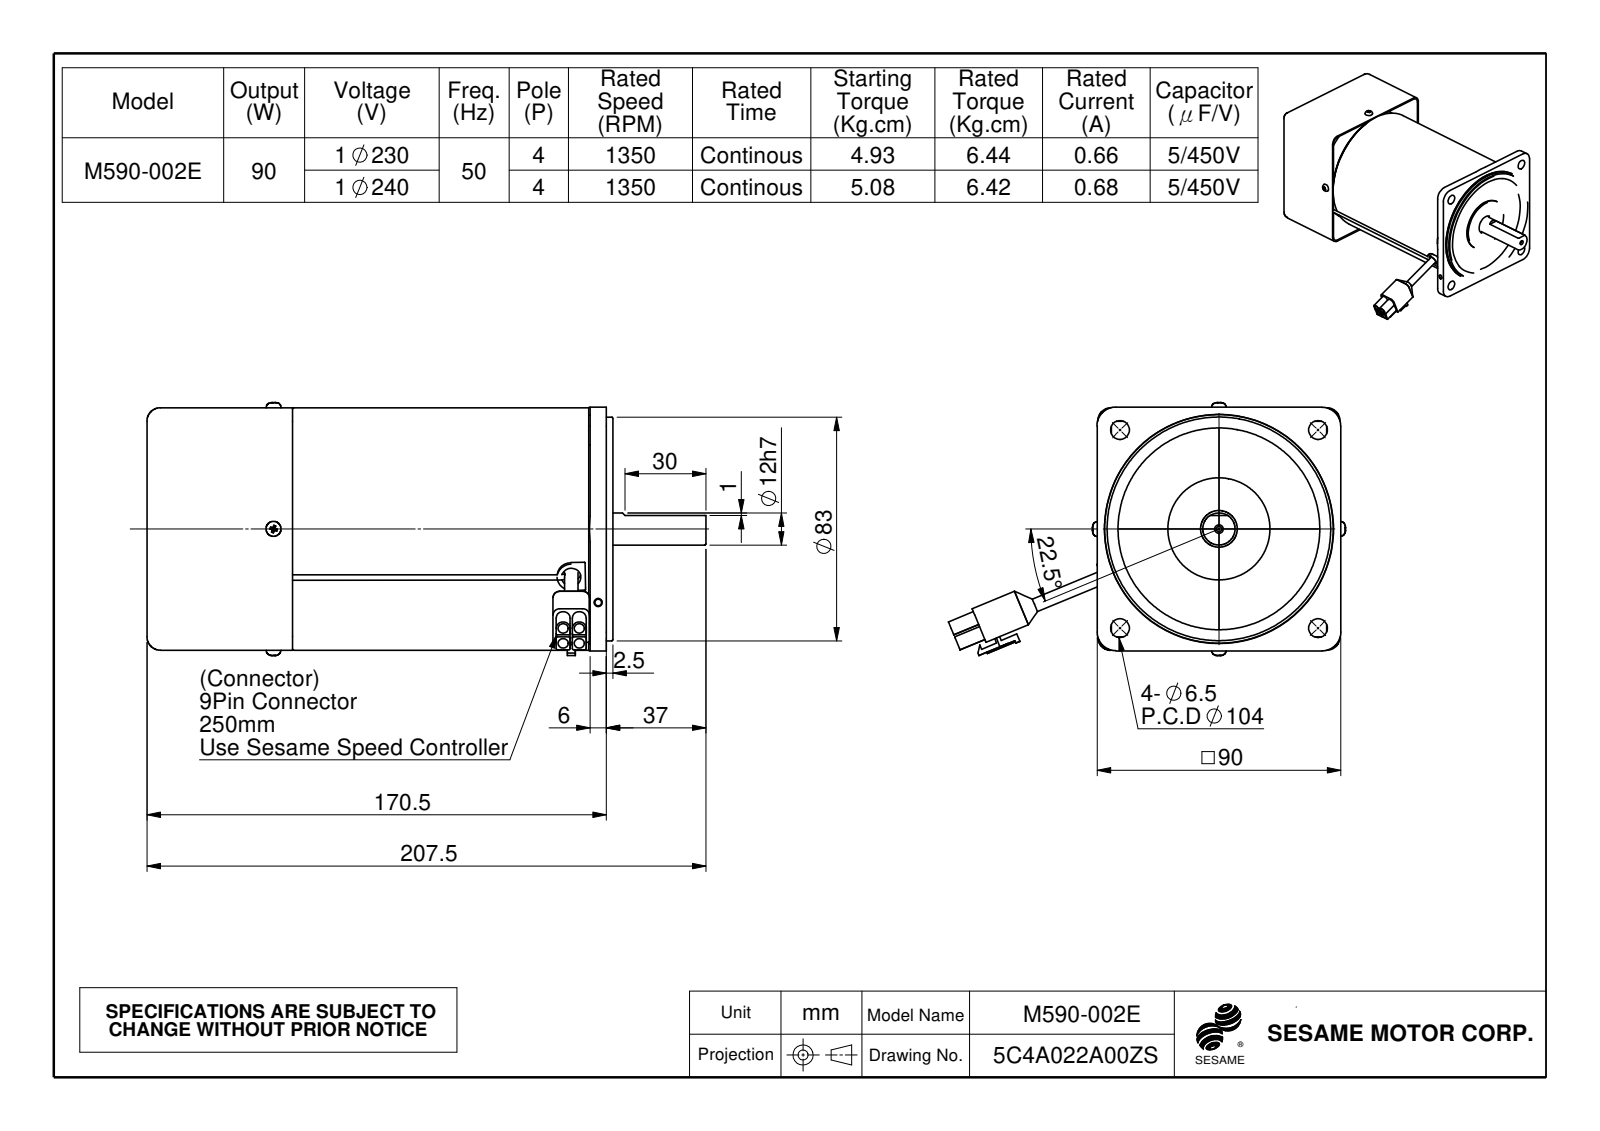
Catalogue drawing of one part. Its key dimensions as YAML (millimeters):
part_name: "公端子; M590-R-F; 線扣; 獨立風扇220V 3K22200000 (+1 more)"
step_written_by: "SolidWorks 2010 (CONFIG_CONTROL_DESIGN)"
units: millimeters
bodies: {solids: 14, faces: 657, planar: 272, cylindrical: 261, other: 124}
overall_size: [207.5, 147.42, 93.92]
volume: 1075000
surface_area: 148580
round_holes:
  - {diameter: 2.5, count: 5}
  - {diameter: 3.8, count: 4}
  - {diameter: 5.5, count: 4}
  - {diameter: 7, count: 4}
  - {diameter: 2, count: 2}
  - {diameter: 3, count: 2}
  - {diameter: 3.1, count: 2}
  - {diameter: 7.2, count: 1}
  - {diameter: 9.5, count: 1}
  - {diameter: 13.7, count: 1}
  - {diameter: 16, count: 1}
  - {diameter: 26, count: 1}
round_bosses_or_shafts:
  - {diameter: 5.5, count: 4}
  - {diameter: 11, count: 3}
  - {diameter: 3, count: 2}
  - {diameter: 2, count: 2}
  - {diameter: 90, count: 1}
  - {diameter: 87, count: 1}
  - {diameter: 86, count: 1}
  - {diameter: 84.15, count: 1}
partial_cylinders:
  - {radius: 0.3, count: 24}
  - {radius: 0.5, count: 14}
  - {radius: 0.25, count: 8}
  - {radius: 4, count: 8}
  - {radius: 5, count: 8}
  - {radius: 2.5, count: 7}
  - {radius: 1, count: 6}
  - {radius: 2, count: 4}
face_to_face_distances: [1, 89, 4, 5, 84, 85, 90, 88, 29, 12]
hole_center_spacings: [6, 3.6, 4.24, 5.01, 38.18, 52, 73.18, 73.54]
